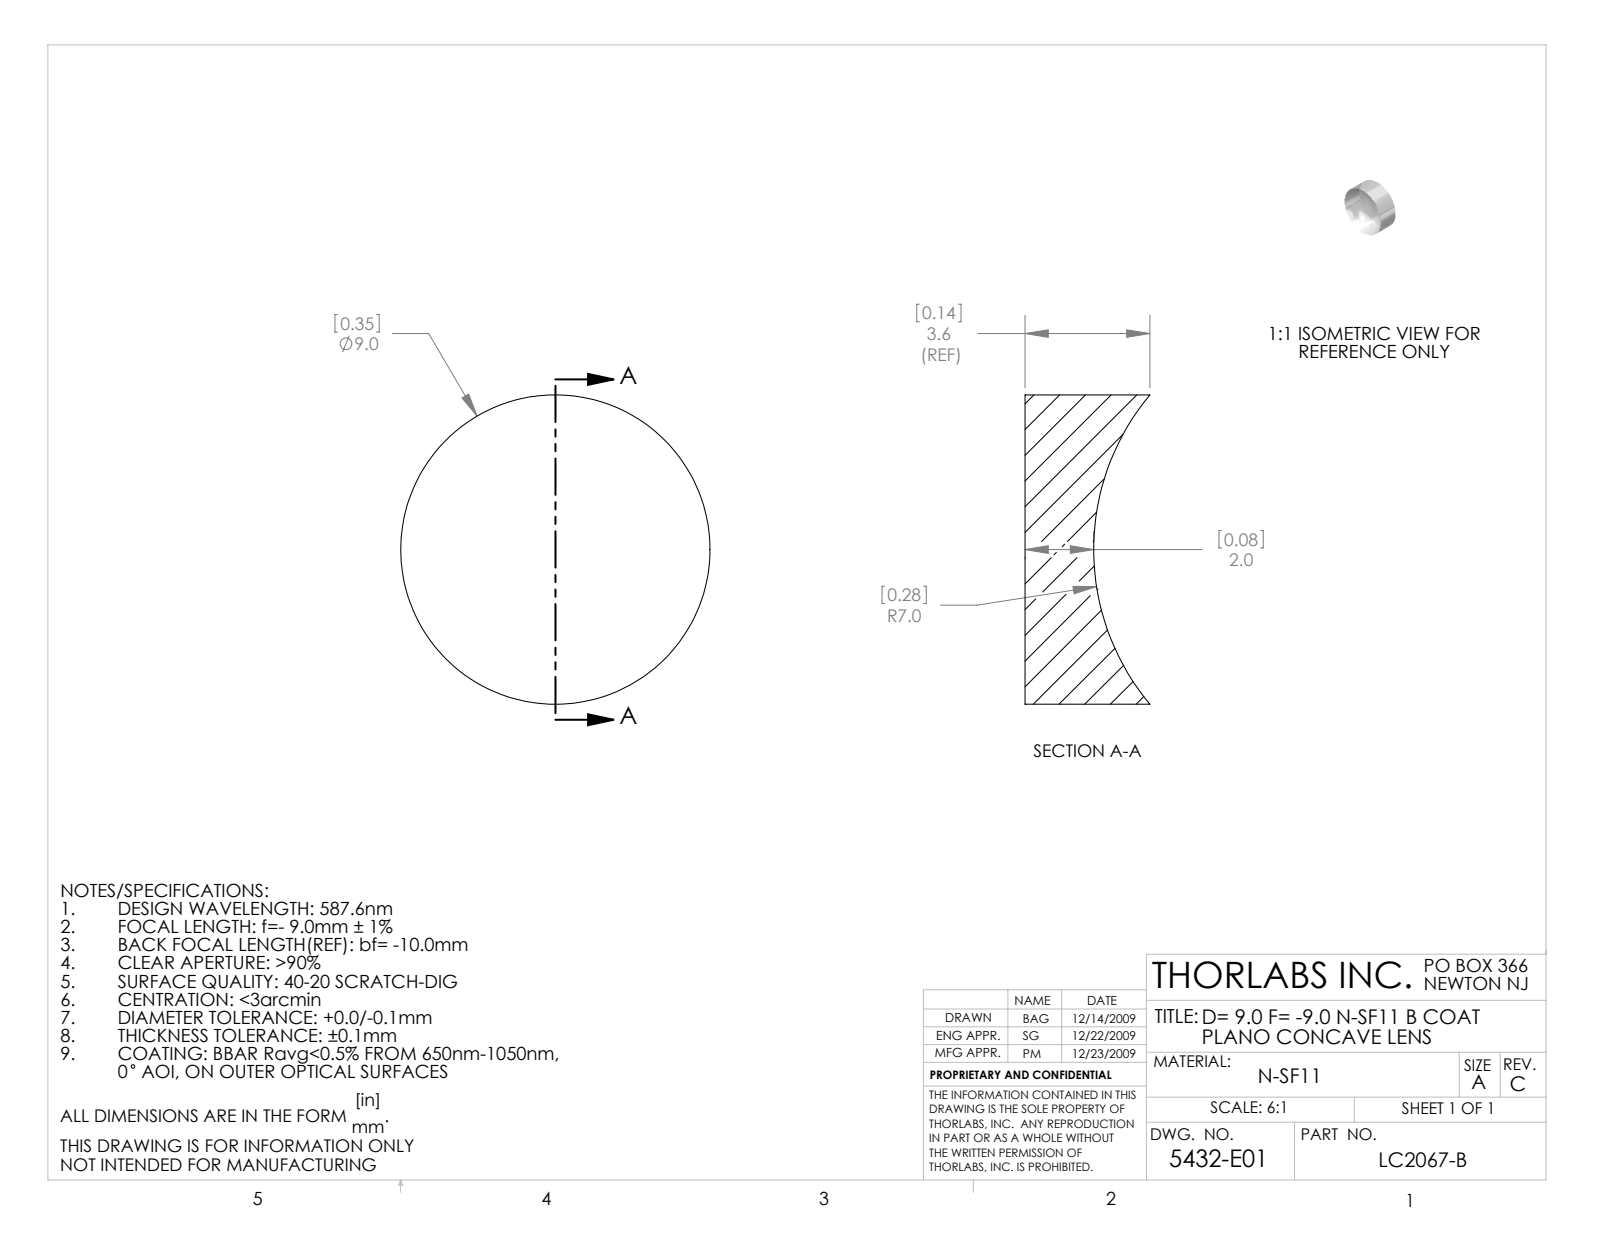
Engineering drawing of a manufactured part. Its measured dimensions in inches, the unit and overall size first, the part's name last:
Units: inches
Overall size (bounding box): 0.354 × 0.354 × 0.143
Round bosses / shafts (diameter × count): ⌀0.354 ×1
Volume: 0.011 in³ · Surface area: 0.37 in²
Bodies: 1 solid, 5 faces (1 planar, 2 cylindrical, 2 other)
Part name (STEP PRODUCT): 5432-E0W
STEP written by: SolidWorks 2009 (AUTOMOTIVE_DESIGN)
